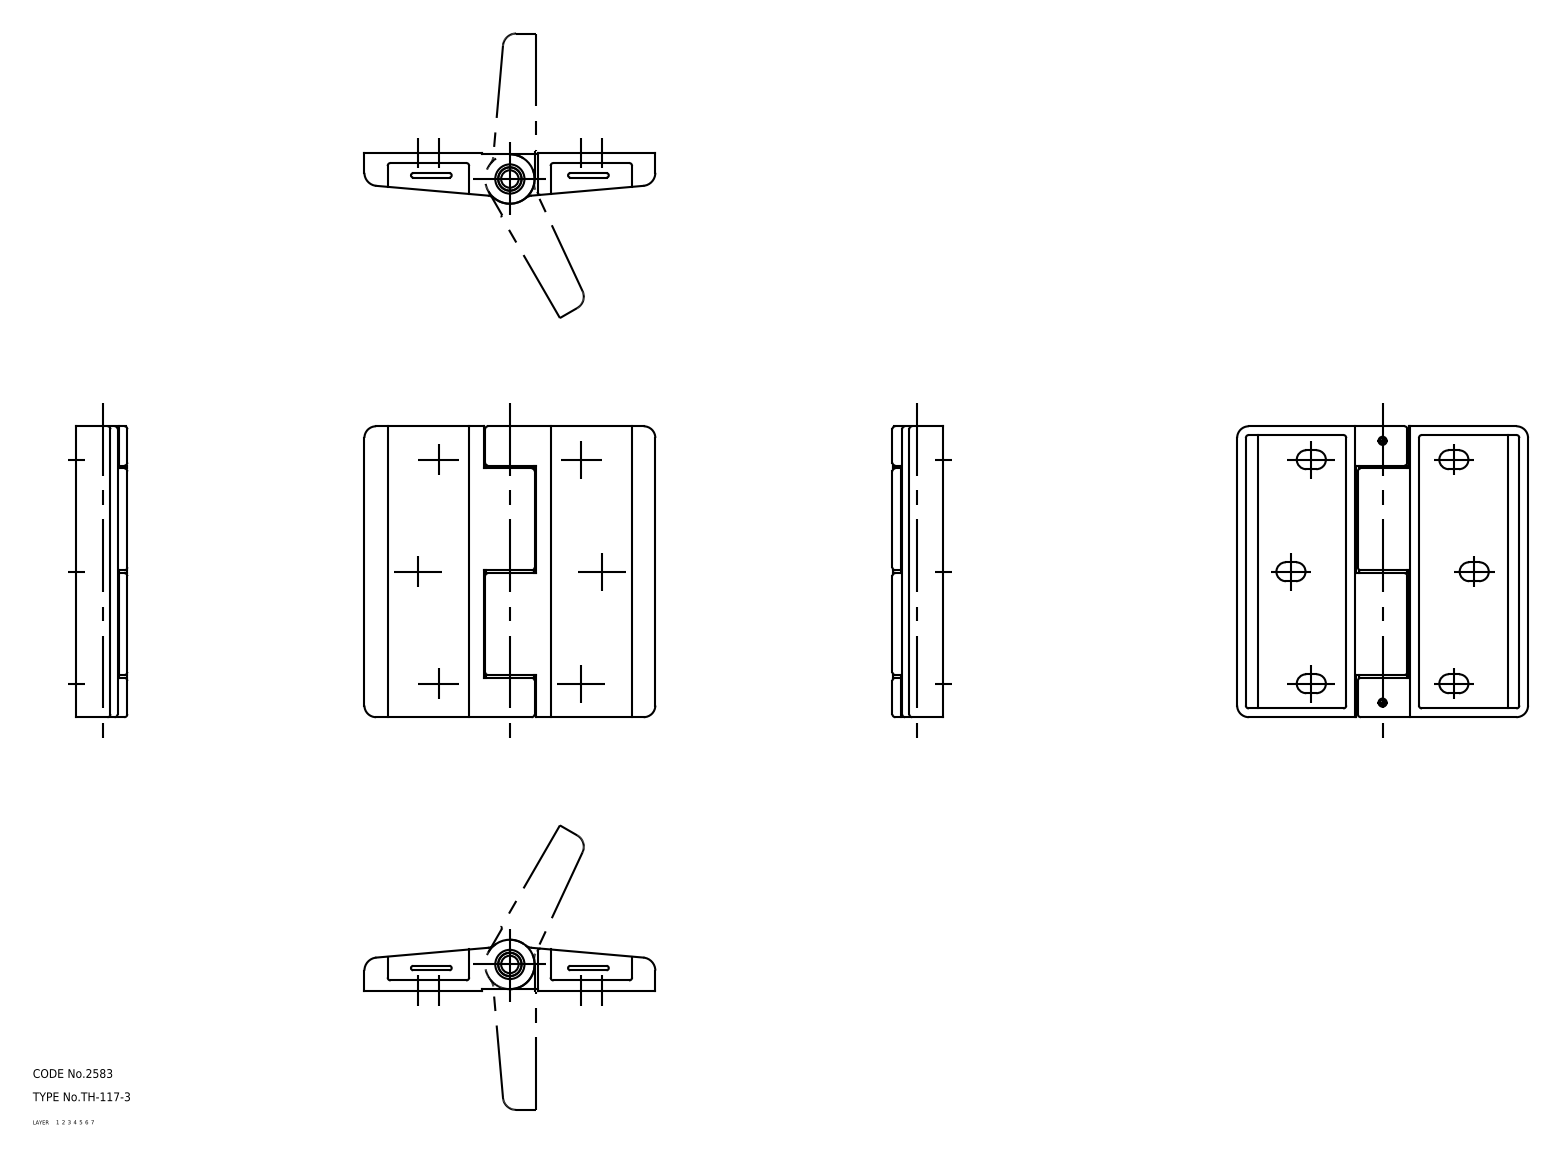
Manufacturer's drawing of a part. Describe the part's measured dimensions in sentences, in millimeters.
The part is named "washer; cover; hinge piece; shaft (+1 more)". Its 3-D file was written by "CADfix (AUTOMOTIVE_DESIGN)". It is 8 solids with 284 faces: 0 planar, 0 cylindrical and 284 other. Overall it measures 100 by 100 by 17.5 millimeters. Its volume is 80 853 cubic millimeters and its surface area 53 426 square millimeters.
